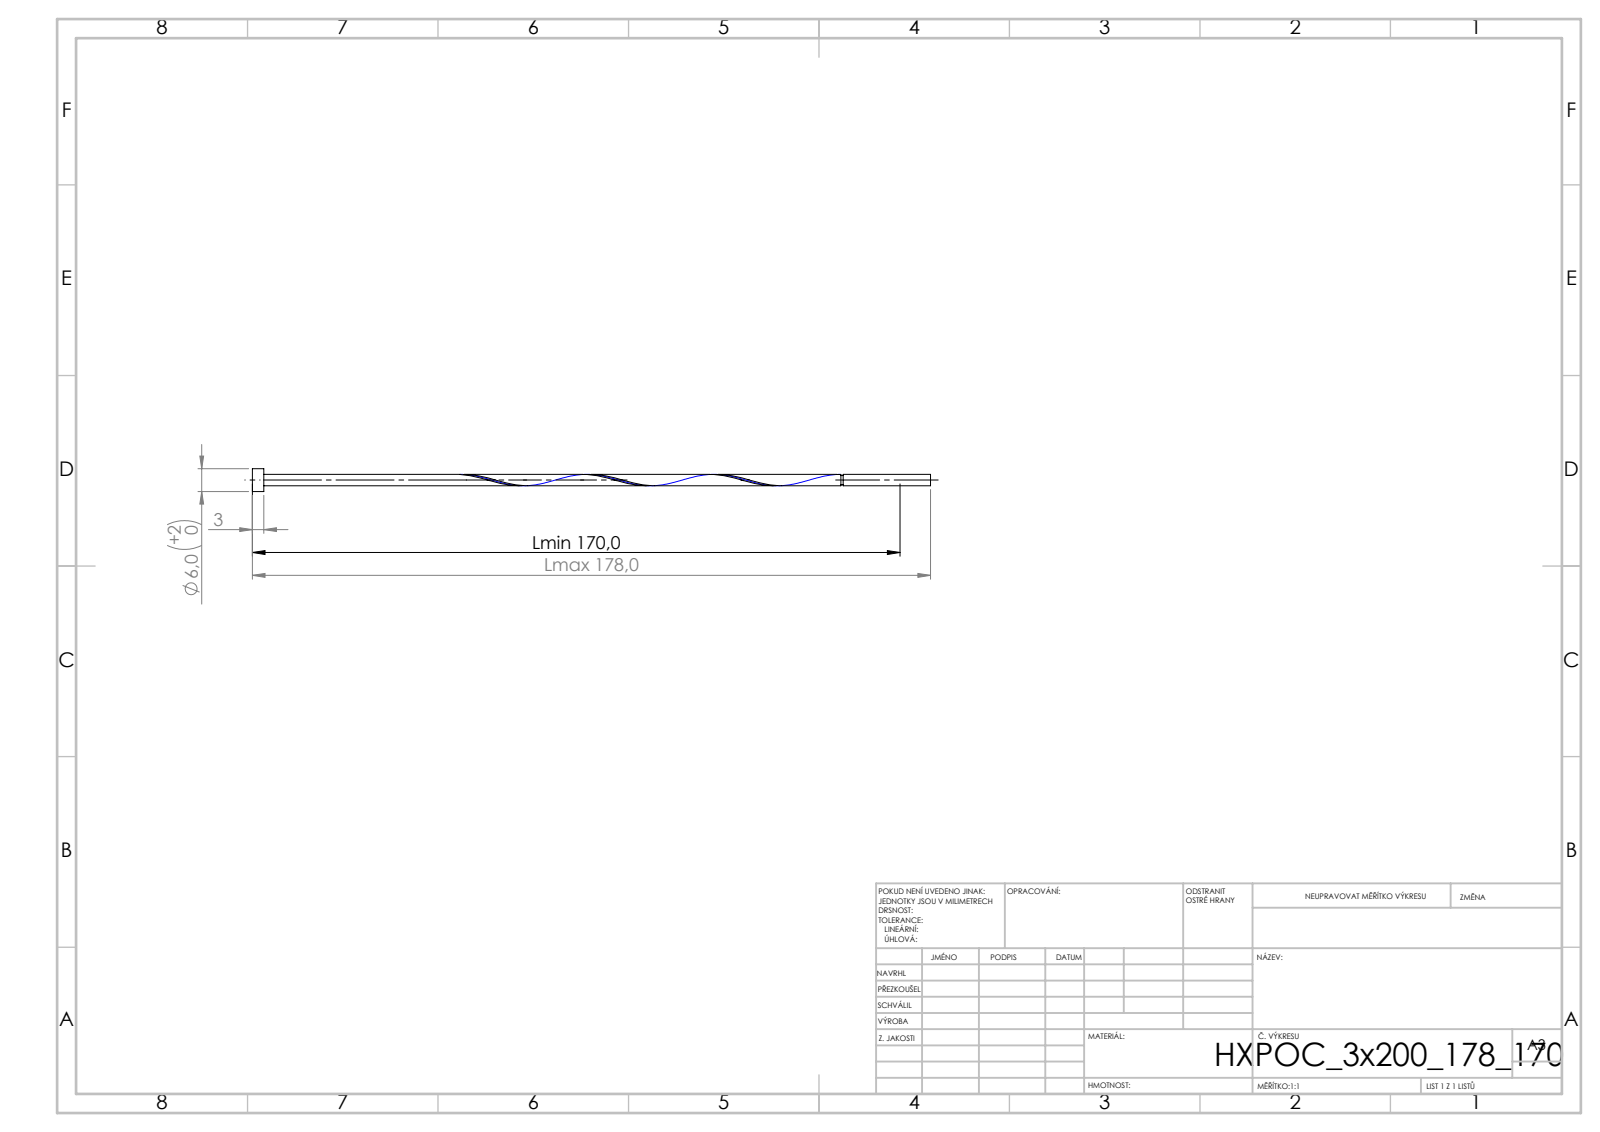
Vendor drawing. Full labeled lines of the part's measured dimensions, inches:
STEP written by: SolidWorks 2019 (CONFIG_CONTROL_DESIGN)
Units: inches
Bodies: 1 solid, 16 faces (6 planar, 9 cylindrical, 1 other)
Overall size (bounding box): 7.008 × 0.236 × 0.236
Volume: 0.099 in³ · Surface area: 3.759 in²
Round bosses / shafts (diameter × count): ⌀0.236 ×1, ⌀0.118 ×1, ⌀0.094 ×1
Main face-to-face distances: 0.118, 7.008, 6.89, 6.106, 5.988, 0.902, 6.082, 5.964, 0.024, 0.926
